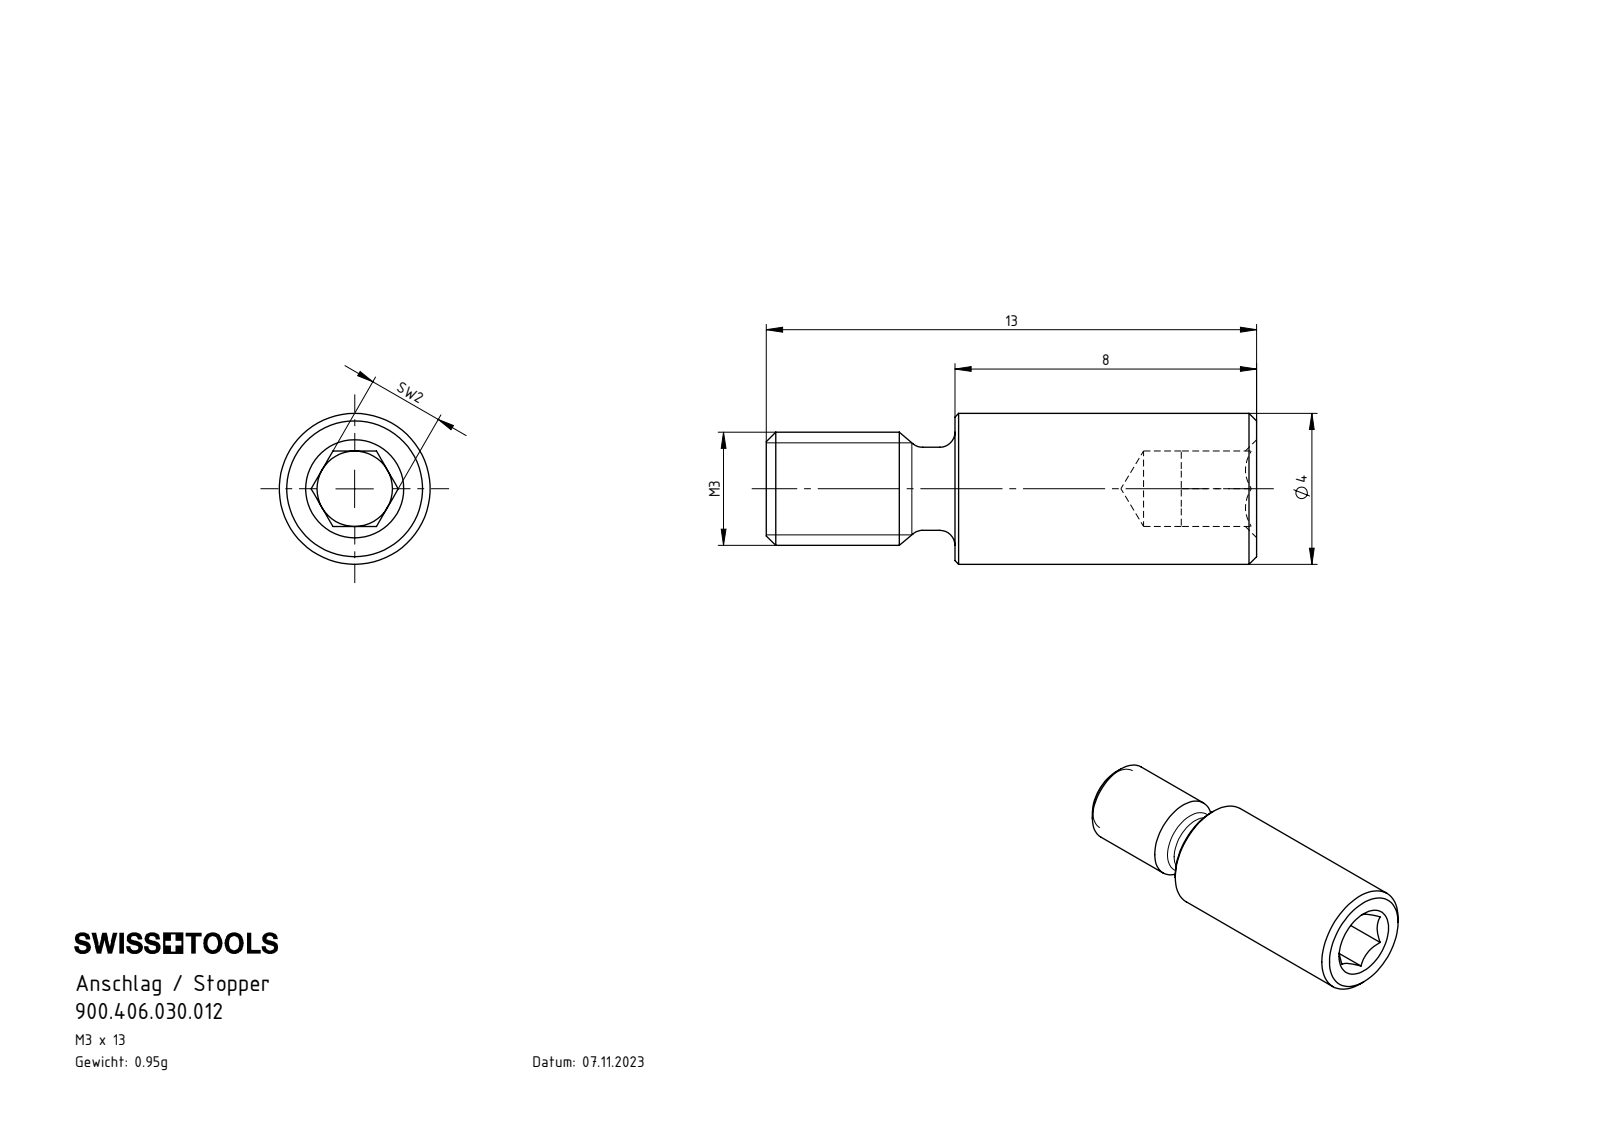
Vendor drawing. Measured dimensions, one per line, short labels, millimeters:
name: 900.406.030.012
written by: SolidWorks 2022 (AUTOMOTIVE_DESIGN)
unit: mm
bodies: 1 solid, 39 faces (15 planar, 8 cylindrical, 16 other)
size: 13 × 4 × 4
volume: 121 mm³; area: 189 mm²
holes: 1× ⌀2
bosses: 1× ⌀4, 1× ⌀3, 1× ⌀2.2
face distances: 2, 13, 5, 8, 11, 6
